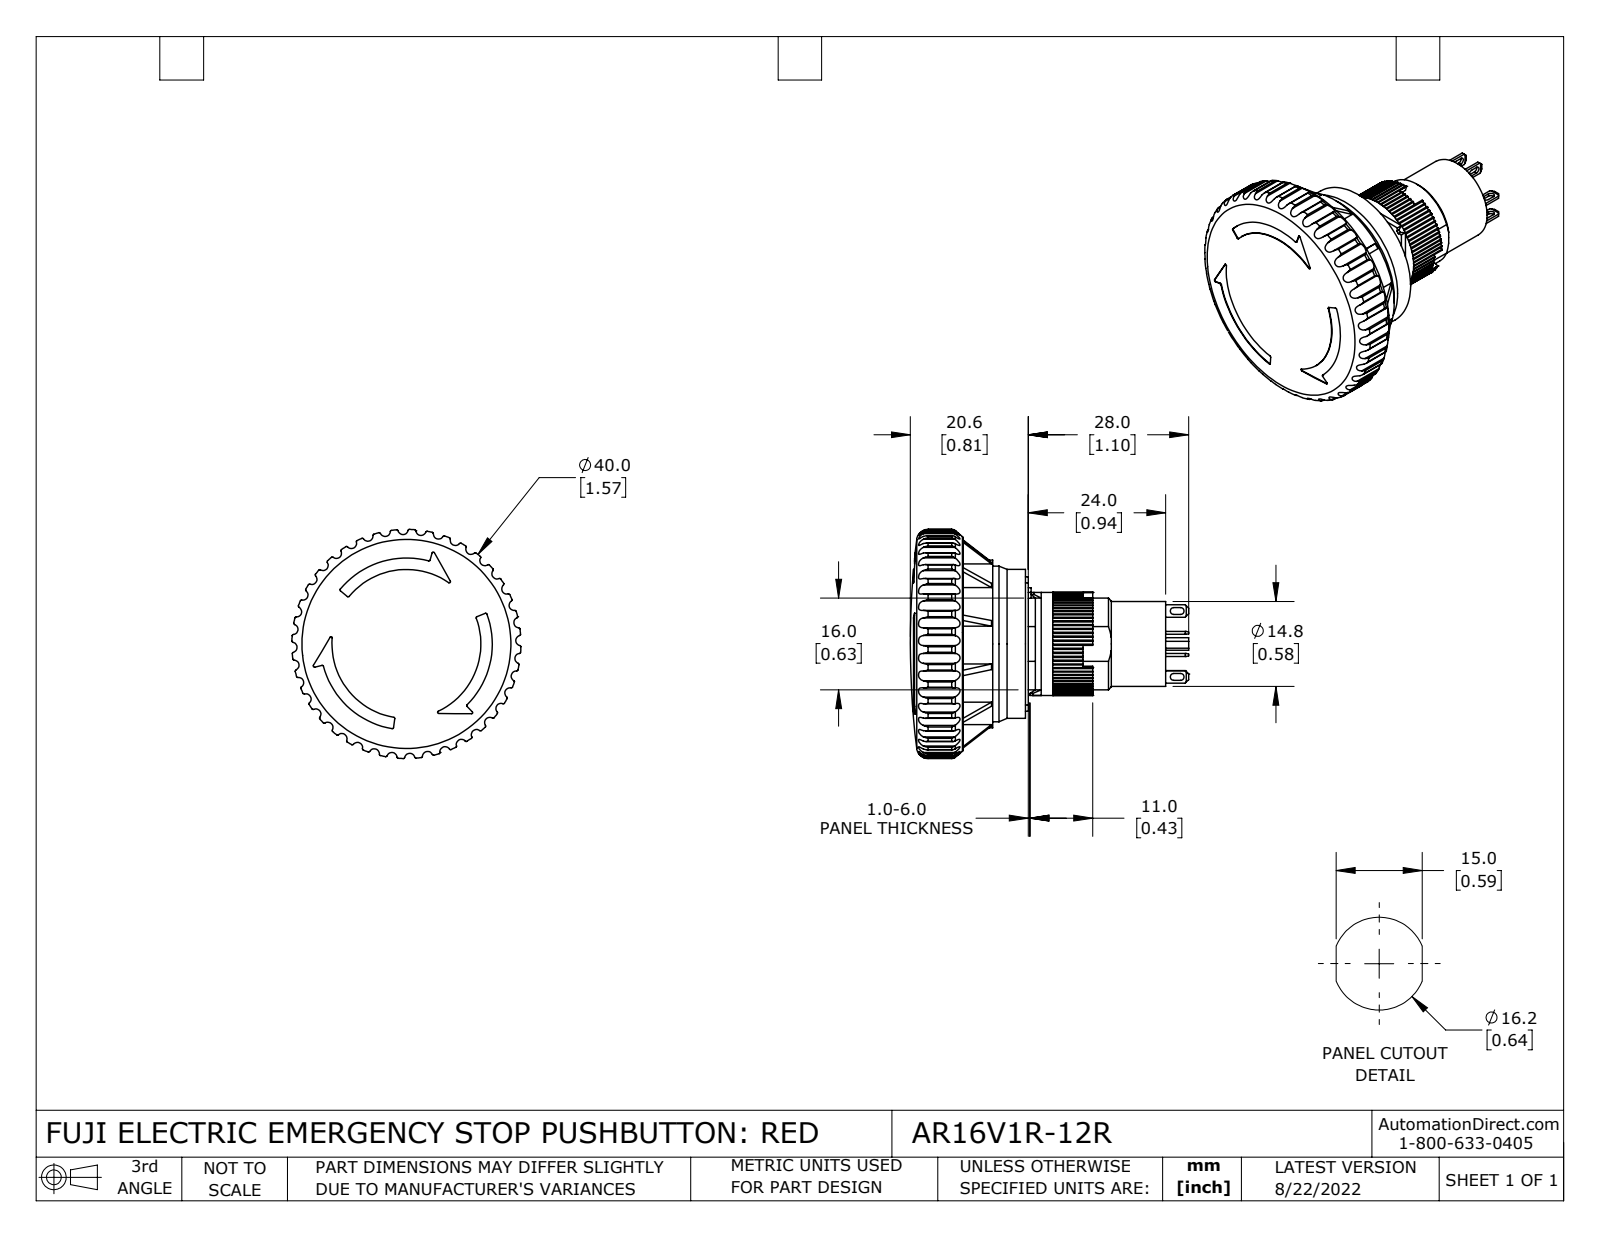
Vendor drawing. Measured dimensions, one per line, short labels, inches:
name: AR16V1R-12R
written by: SolidWorks 2021 (CONFIG_CONTROL_DESIGN)
unit: in
bodies: 5 solids, 1001 faces (495 planar, 410 cylindrical, 96 other)
size: 1.913 × 1.575 × 1.575
volume: 0.963 in³; area: 19.04 in²
holes: 1× ⌀0.583, 1× ⌀0.63, 1× ⌀0.709, 1× ⌀1.069, 1× ⌀1.433
bosses: 1× ⌀1.154, 1× ⌀1.024, 1× ⌀0.858, 1× ⌀0.236
rounds: 80× R0.008, 80× R0.01, 40× R0.035, 8× R0.02, 8× R0.024, 2× R0.039, 1× R0.031, 1× R0.114
face distances: 0.039, 0.421, 0.53, 0.108, 0.02, 0.069, 0.856, 0.49, 0.089, 0.049
